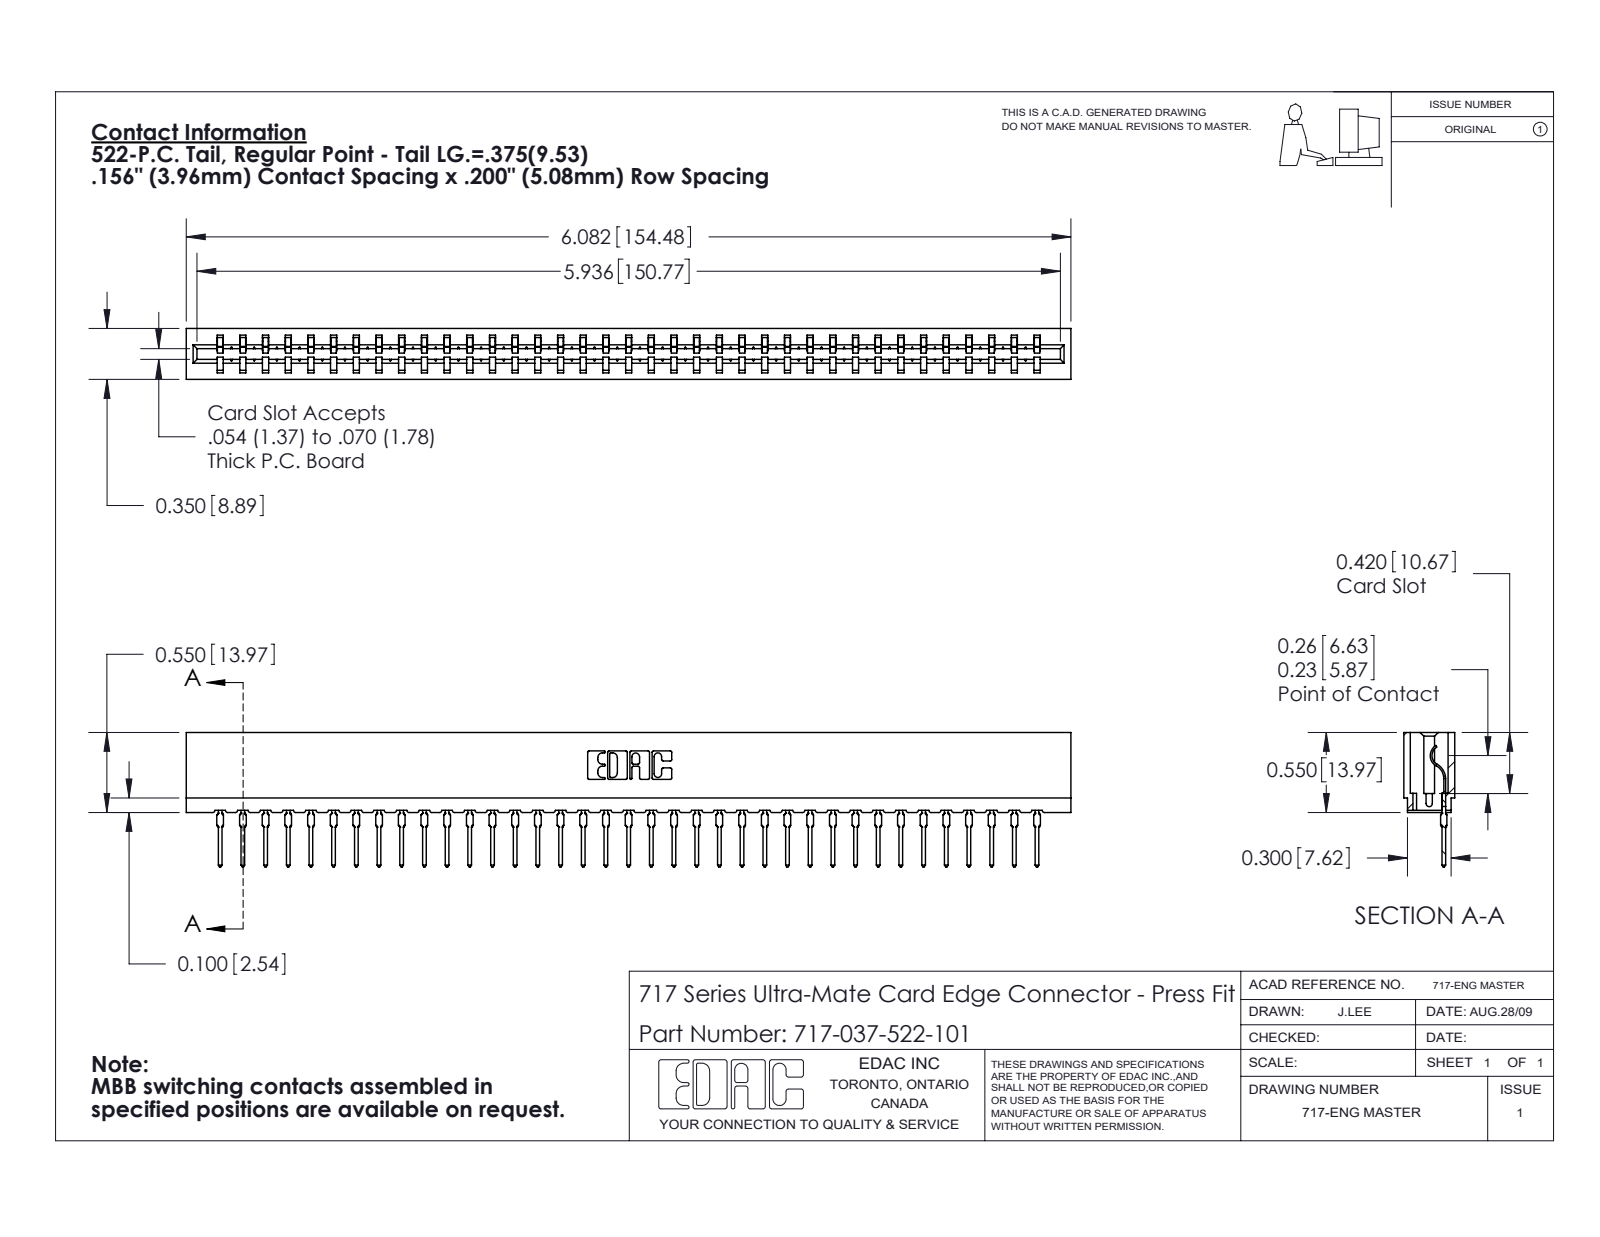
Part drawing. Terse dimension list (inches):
name: 745-292-001_522; 717-037-522-101; 717 Part_Insulator Option - 06
written by: SolidWorks 2020 (CONFIG_CONTROL_DESIGN)
unit: in
bodies: 38 solids, 4275 faces (2570 planar, 743 cylindrical, 962 other)
size: 6.082 × 0.924 × 0.35
volume: 0.798 in³; area: 28.53 in²
rounds: 74× R0.015, 74× R0.021, 22× R0.01, 6× R0.007, 6× R0.031, 4× R0.005, 4× R0.011, 3× R0.026
face distances: 0.212, 0.138, 0.35, 0.074, 0.045, 0.305, 0.093, 0.167, 0.063, 0.287
